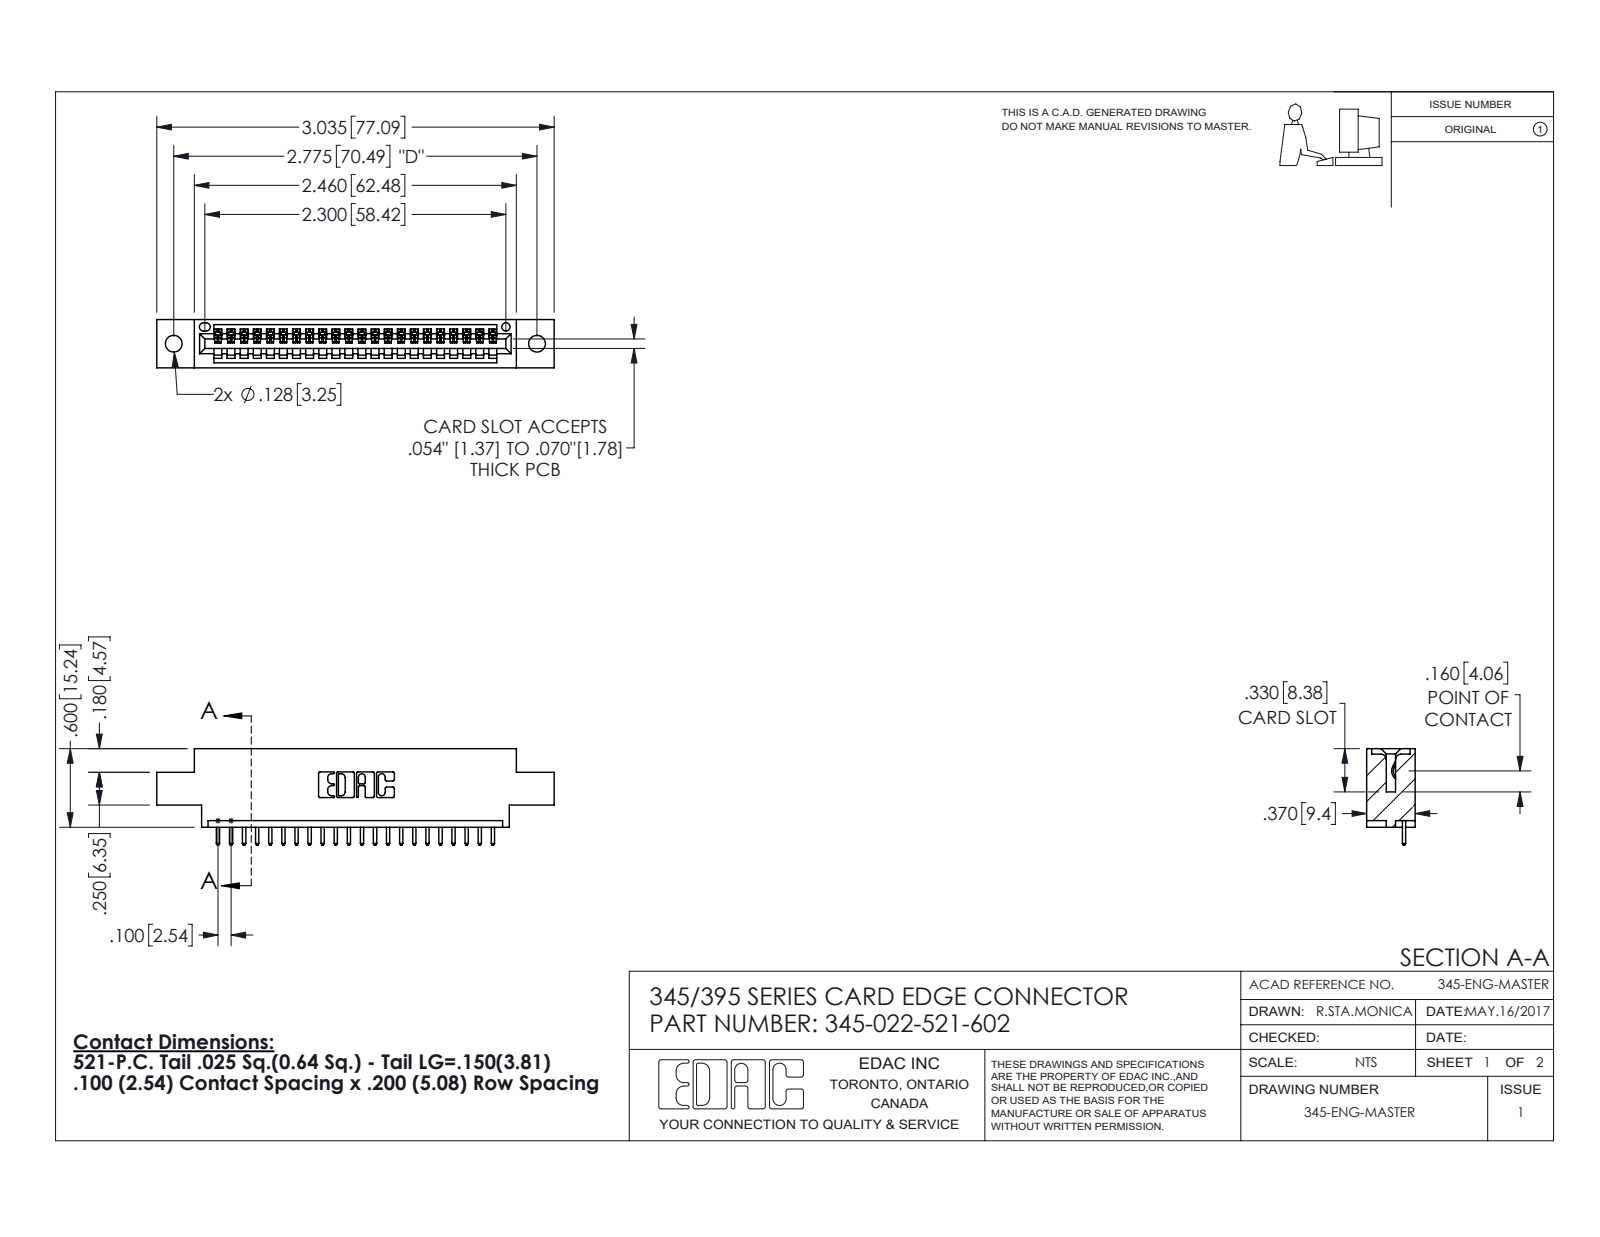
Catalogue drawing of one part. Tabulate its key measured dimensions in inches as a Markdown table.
| quantity | value |
| --- | --- |
| part name | 345-292-001_345-293-121; 345 Part_0.170 Offset - 0.128 Dia; 345-022-521-602 |
| STEP written by | SolidWorks 2016 (CONFIG_CONTROL_DESIGN) |
| units | inches |
| bodies | 23 solids, 1406 faces (964 planar, 442 cylindrical, 0 other) |
| overall size | 3.035 × 0.737 × 0.37 |
| volume | 0.424 in³ |
| surface area | 13.28 in² |
| round holes (diameter × count) | 0.128 × 2, 0.064 × 1 |
| partial cylindrical surfaces (radius × count) | 0.006 × 44, 0.01 × 44, 0.01 × 22, 0.007 × 6, 0.031 × 6, 0.026 × 3, 0.031 × 2, 0.04 × 2 |
| main face-to-face distances | 0.298, 0.072, 0.37, 0.2, 0.098, 0.272, 0.025, 0.225, 0.175, 0.15 |
| hole center spacings | 0.27, 2.541, 2.775 |
